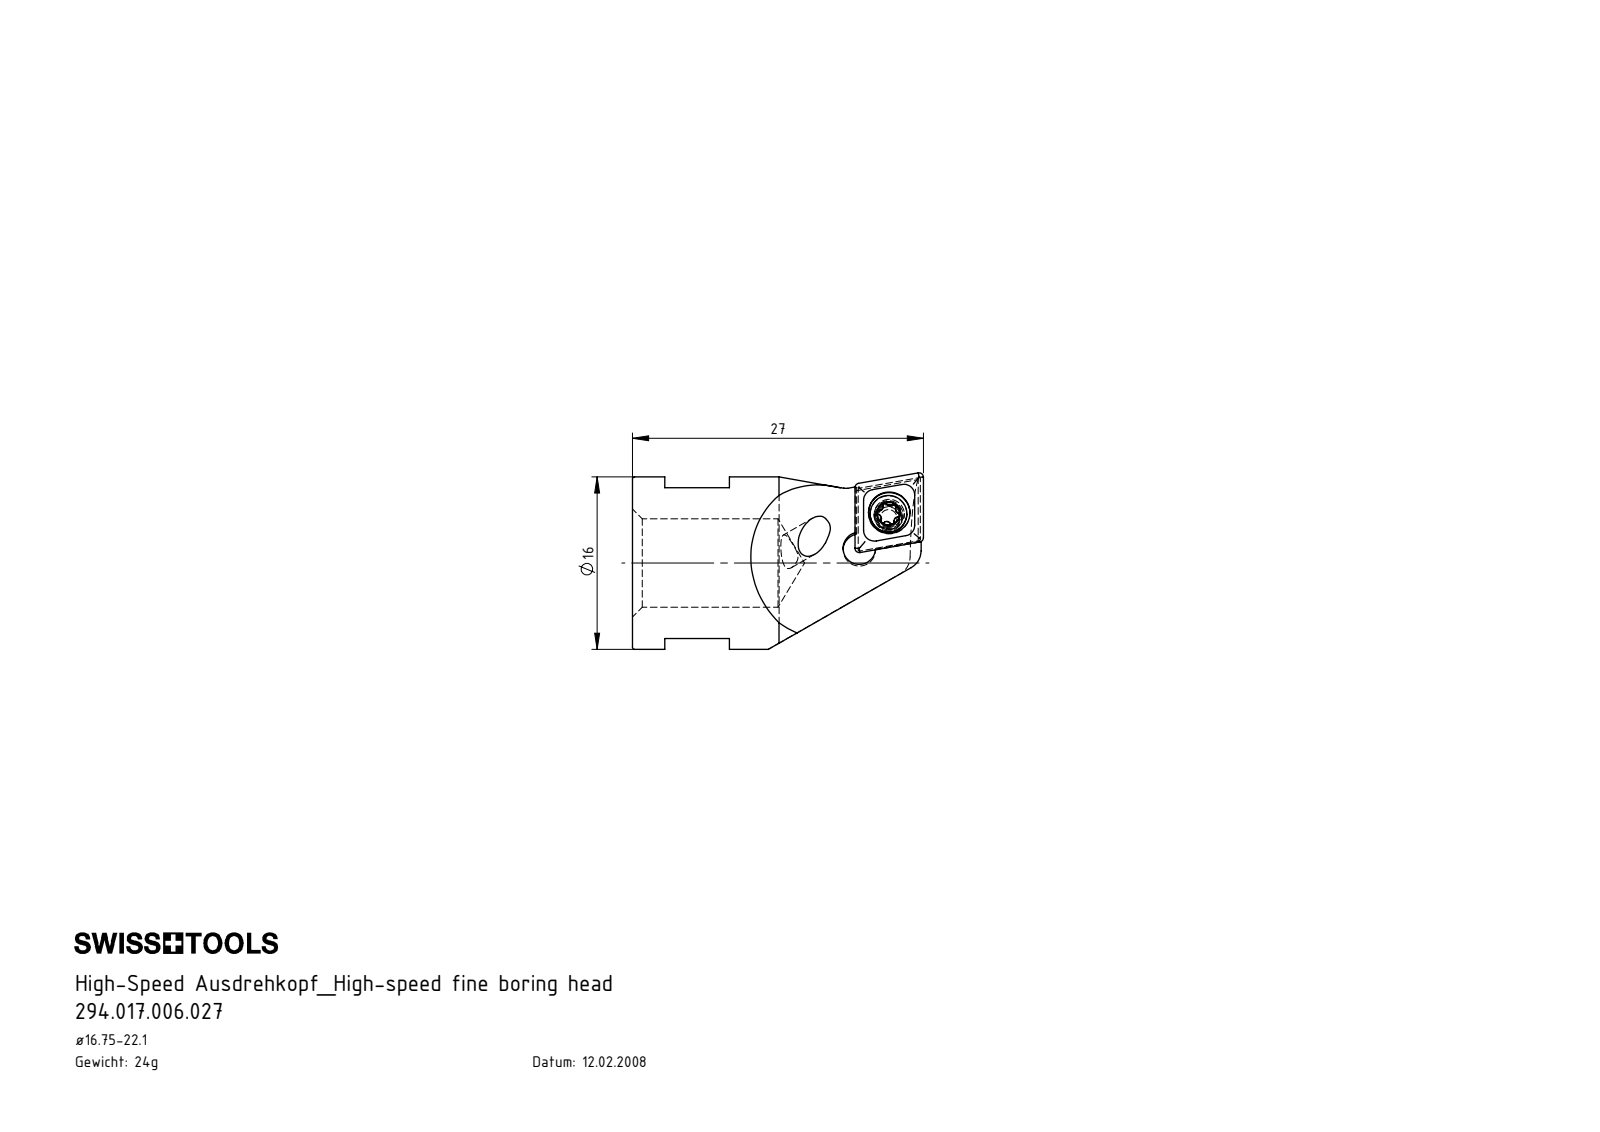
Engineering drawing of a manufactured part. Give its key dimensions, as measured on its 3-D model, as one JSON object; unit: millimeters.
{"part_name": "WCA-ER2.001.006_A; CCMT060204; HS0-A17.K11.027_B; HS0.A17.K11.027", "step_written_by": "SolidWorks 2017 (AUTOMOTIVE_DESIGN)", "units": "millimeters", "bodies": {"solids": 3, "faces": 96, "planar": 33, "cylindrical": 23, "other": 40}, "overall_size": [27, 16.38, 16], "volume_mm3": 2960, "surface_area_mm2": 1990, "round_holes": [[2.05, 1], [2.8, 1], [3, 1], [3.85, 1], [8.2, 1]], "round_bosses_or_shafts": [[16, 1], [3.4, 1], [2.5, 1]], "partial_cylinders_radius": [[0.21, 6], [0.36, 3], [0.36, 3], [1.5, 1], [1.8, 1], [2, 1]], "face_to_face_distances": [14, 2.28, 6, 2.38, 9, 3, 20.8, 17.8, 11.8, 1.48]}
